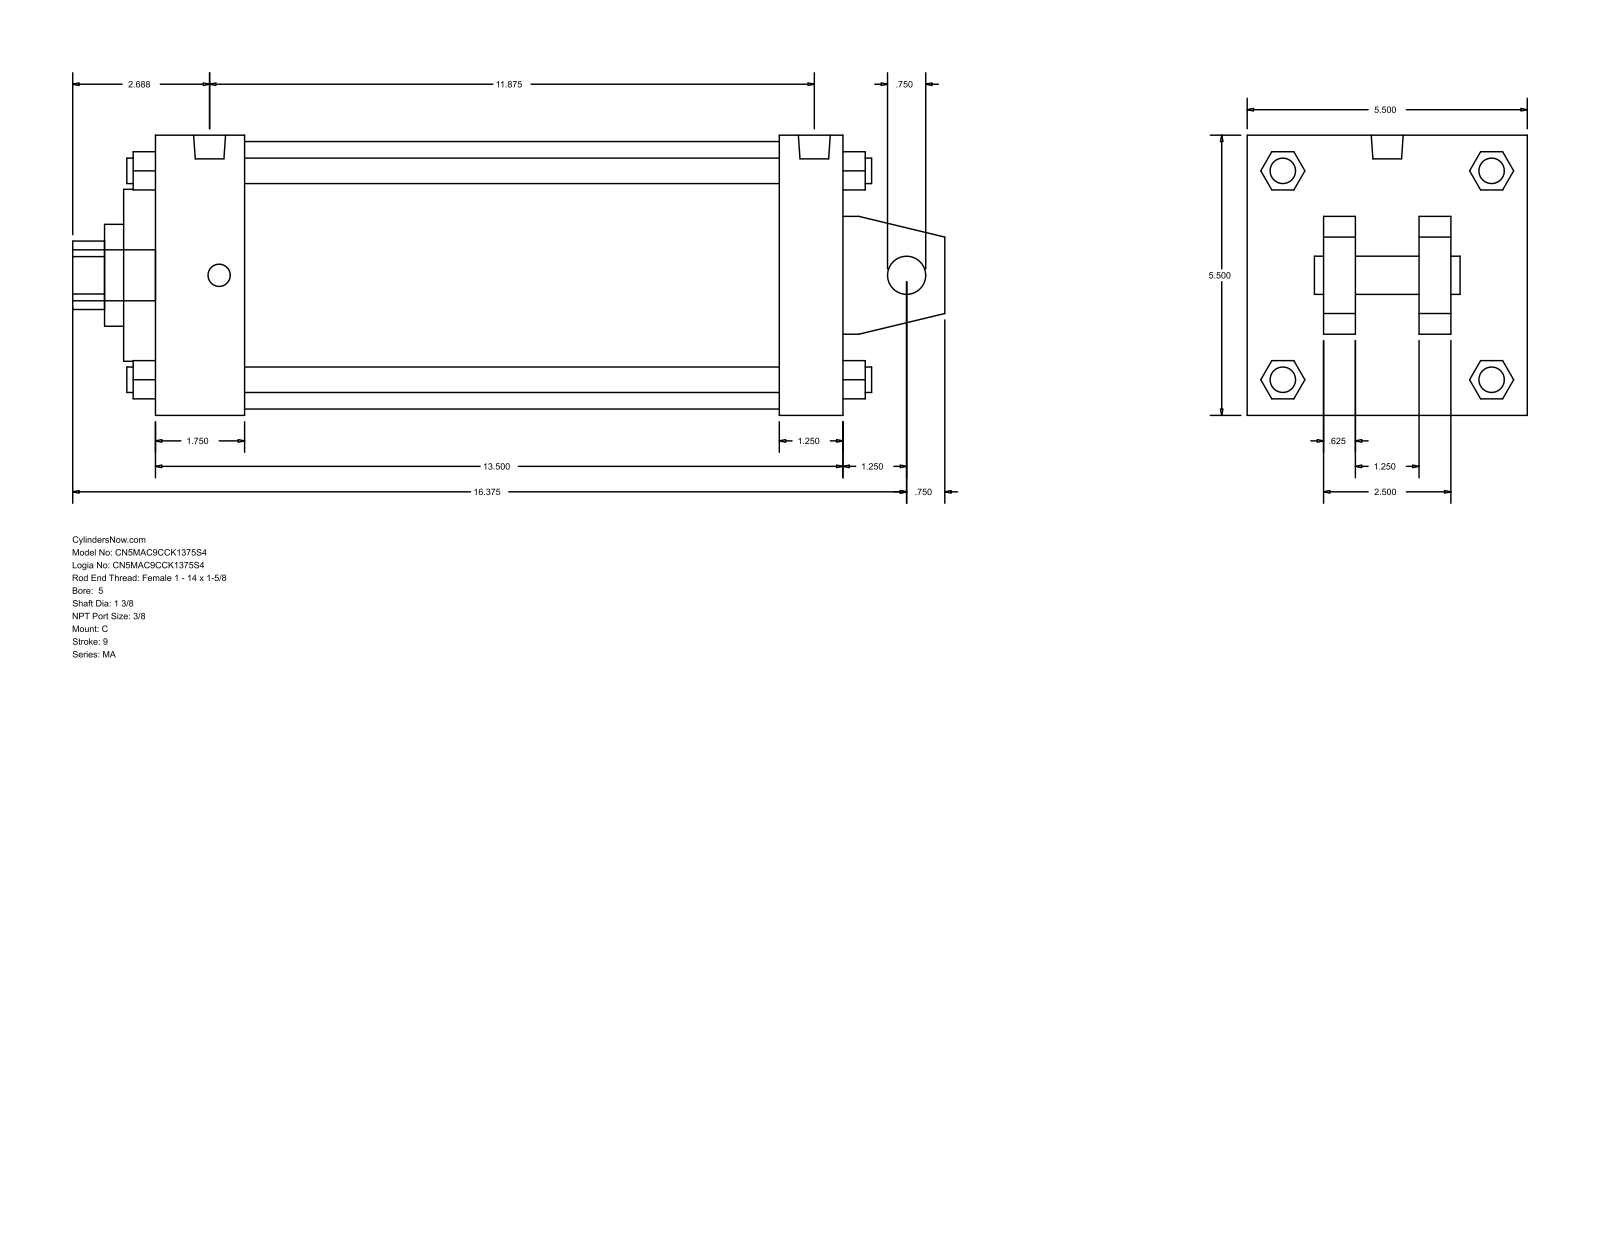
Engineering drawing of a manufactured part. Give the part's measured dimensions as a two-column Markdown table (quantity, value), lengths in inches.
| quantity | value |
| --- | --- |
| part name | MA_C__0500_1.375 |
| STEP written by | GSSL Pune (CONFIG_CONTROL_DESIGN) |
| units | inches |
| bodies | 0 solids, 141 faces (109 planar, 32 cylindrical, 0 other) |
| overall size | 17.125 × 5.5 × 5.5 |
| round holes (diameter × count) | 0.75 × 1, 1.375 × 1, 2 × 1, 3.375 × 1, 5.25 × 1 |
| round bosses / shafts (diameter × count) | 0.5 × 4, 0.437 × 4, 0.627 × 2, 1 × 1 |
| partial cylindrical surfaces (radius × count) | 0.672 × 1 |
| main face-to-face distances | 5.5, 13.5, 0.625, 12.25, 1.25, 1.75, 10.5, 11.75, 1.5, 4 |
